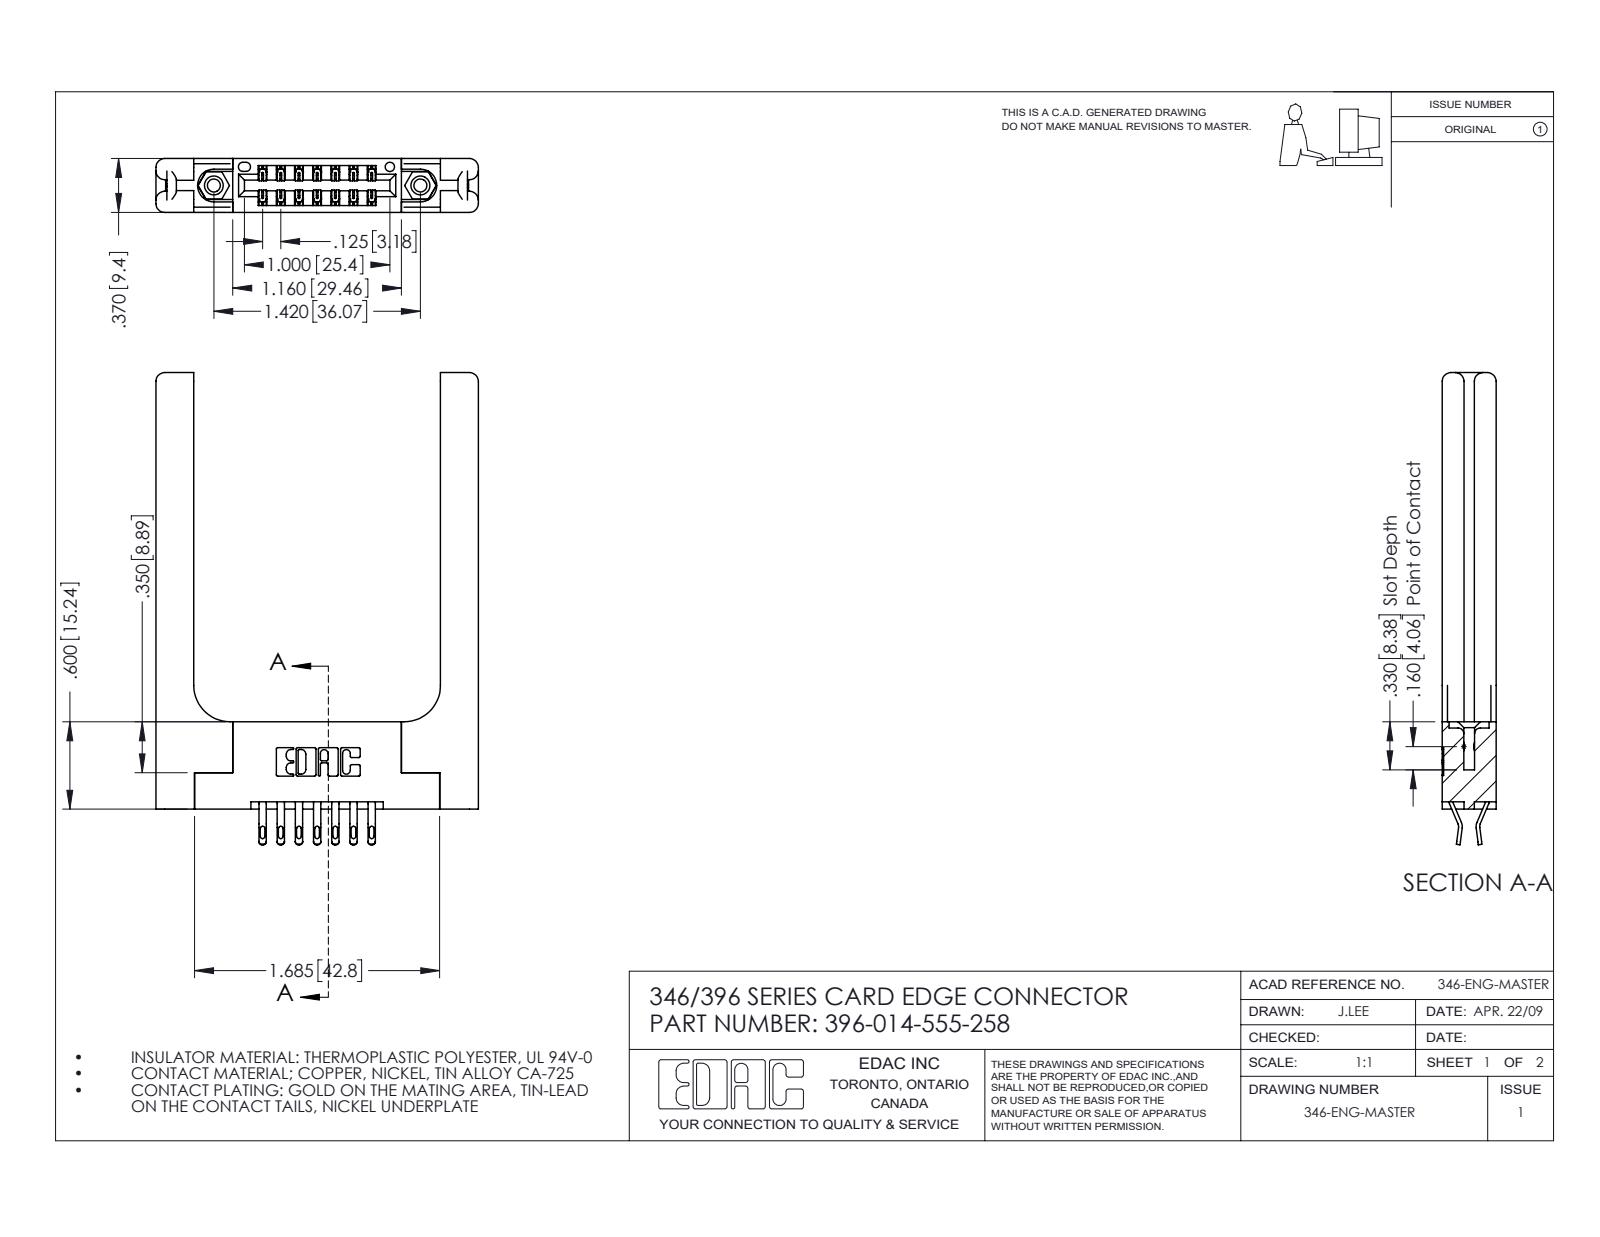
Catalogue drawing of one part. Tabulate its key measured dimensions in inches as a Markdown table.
| quantity | value |
| --- | --- |
| part name | 346 Part_Flush Mounting Lugs - 0.156 Dia-TH; 396-014-555-258; 345-250-001_345-250-001-102; 345-292-001_555 Tail (+1 more) |
| STEP written by | SolidWorks 2016 (CONFIG_CONTROL_DESIGN) |
| units | inches |
| bodies | 19 solids, 1190 faces (686 planar, 444 cylindrical, 60 other) |
| overall size | 3.245 × 2.216 × 0.37 |
| volume | 0.778 in³ |
| surface area | 18.28 in² |
| round holes (diameter × count) | 0.089 × 2, 0.125 × 2, 0.156 × 2, 0.064 × 1 |
| round bosses / shafts (diameter × count) | 0.155 × 2 |
| partial cylindrical surfaces (radius × count) | 0.016 × 28, 0.02 × 28, 0.01 × 22, 0.006 × 21, 0.06 × 16, 0.007 × 6, 0.031 × 6, 0.026 × 3 |
| main face-to-face distances | 0.37, 0.15, 0.22, 0.072, 0.25, 0.148, 1.696, 0.102, 0.048, 0.322 |
| hole center spacings | 0.246, 1.217, 1.42 |
